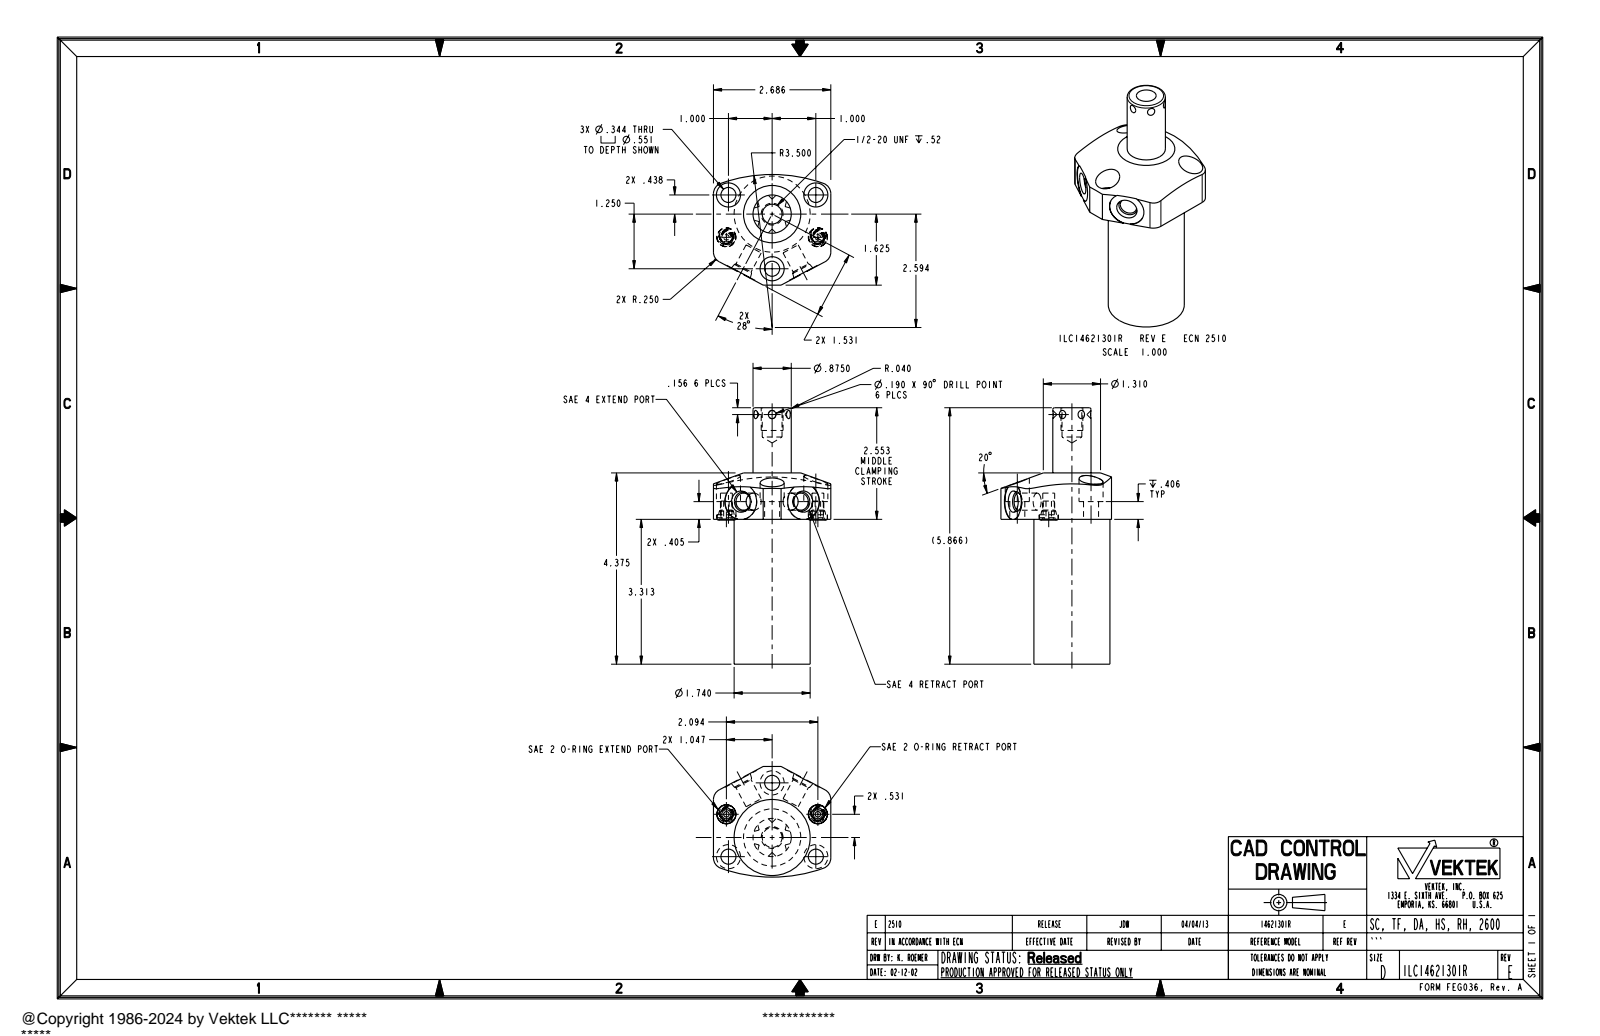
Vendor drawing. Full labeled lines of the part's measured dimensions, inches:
Part name (STEP PRODUCT): ILC14621301R
STEP written by: PRO/ENGINEER BY PARAMETRIC TECHNOLOGY CORPORATION, 2007460 (AUTOMOTIVE_DESIGN_CC2)
Units: inches
Bodies: 1 solid, 132 faces (33 planar, 57 cylindrical, 42 other)
Overall size (bounding box): 5.866 × 2.686 × 2.531
Volume: 13.47 in³ · Surface area: 50.56 in²
Round holes (diameter × count): ⌀0.344 ×3, ⌀0.551 ×3, ⌀0.125 ×2, ⌀0.272 ×2, ⌀0.392 ×2, ⌀0.438 ×2, ⌀0.453 ×1
Round bosses / shafts (diameter × count): ⌀0.43 ×2, ⌀0.256 ×2, ⌀0.21 ×2, ⌀1.74 ×1, ⌀0.875 ×1, ⌀0.5 ×1
Partial cylindrical surfaces — rounded edges, fillets, slot ends (radius × count): R0.25 ×4, R0.412 ×2, R3.5 ×1
Main face-to-face distances: 3.313, 2.686, 4.375, 1.062, 3.719, 0.406, 0.656, 5.866, 2.553, 2.147
Hole centre spacings: 0.97, 1.092, 1.174, 1.27, 1.962, 2.265, 1.25, 2
